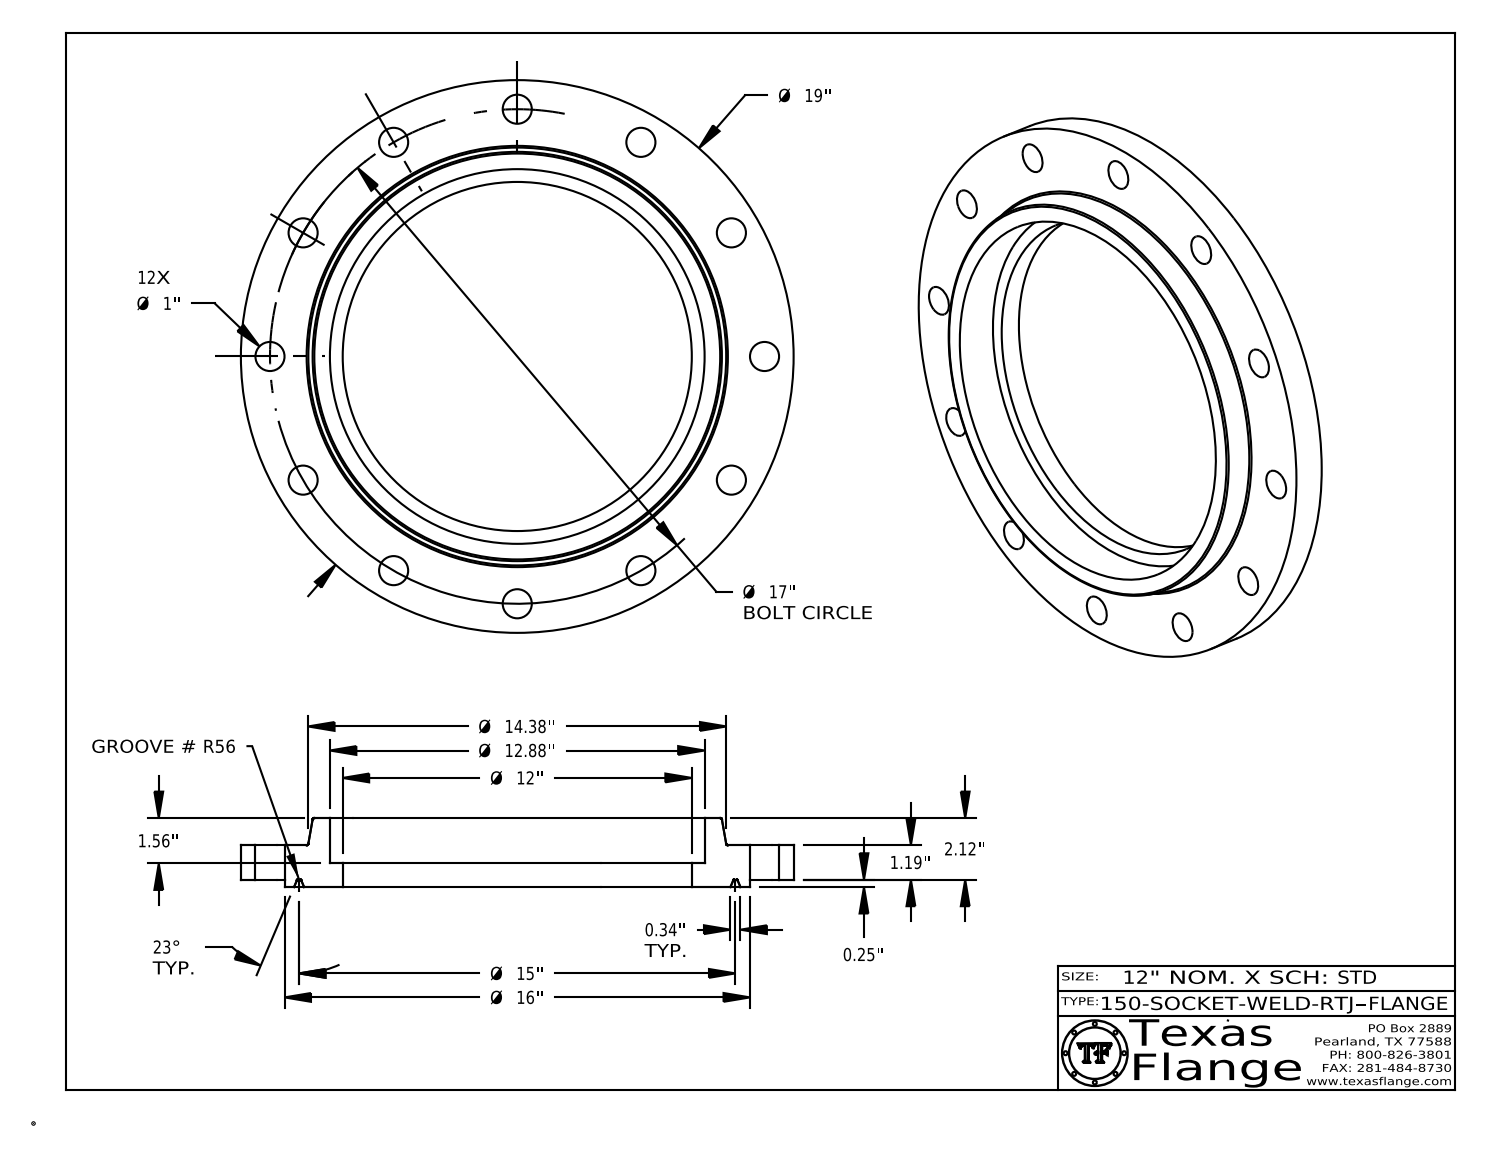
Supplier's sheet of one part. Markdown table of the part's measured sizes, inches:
| quantity | value |
| --- | --- |
| part name | 150-SOCKET-WELD-RTJ |
| STEP written by | CATIA V5 STEP AP214 (AUTOMOTIVE_DESIGN) |
| units | inches |
| bodies | 1 solid, 438 faces (372 planar, 52 cylindrical, 14 other) |
| overall size | 19 × 19 × 2.37 |
| volume | 226.4 in³ |
| surface area | 592.7 in² |
| round holes (diameter × count) | 1 × 12, 0.495 × 1, 12 × 1, 12.88 × 1 |
| round bosses / shafts (diameter × count) | 0.03 × 8, 19 × 1, 16 × 1, 0.39 × 1 |
| main face-to-face distances | 1.19, 0.25, 1.44, 2.37, 2.12, 0.93, 0.81, 0.56, 0.63, 1.56 |
| hole center spacings | 8.5, 16.42, 4.4, 12.02, 14.722, 4.4, 12.021, 14.722 |
